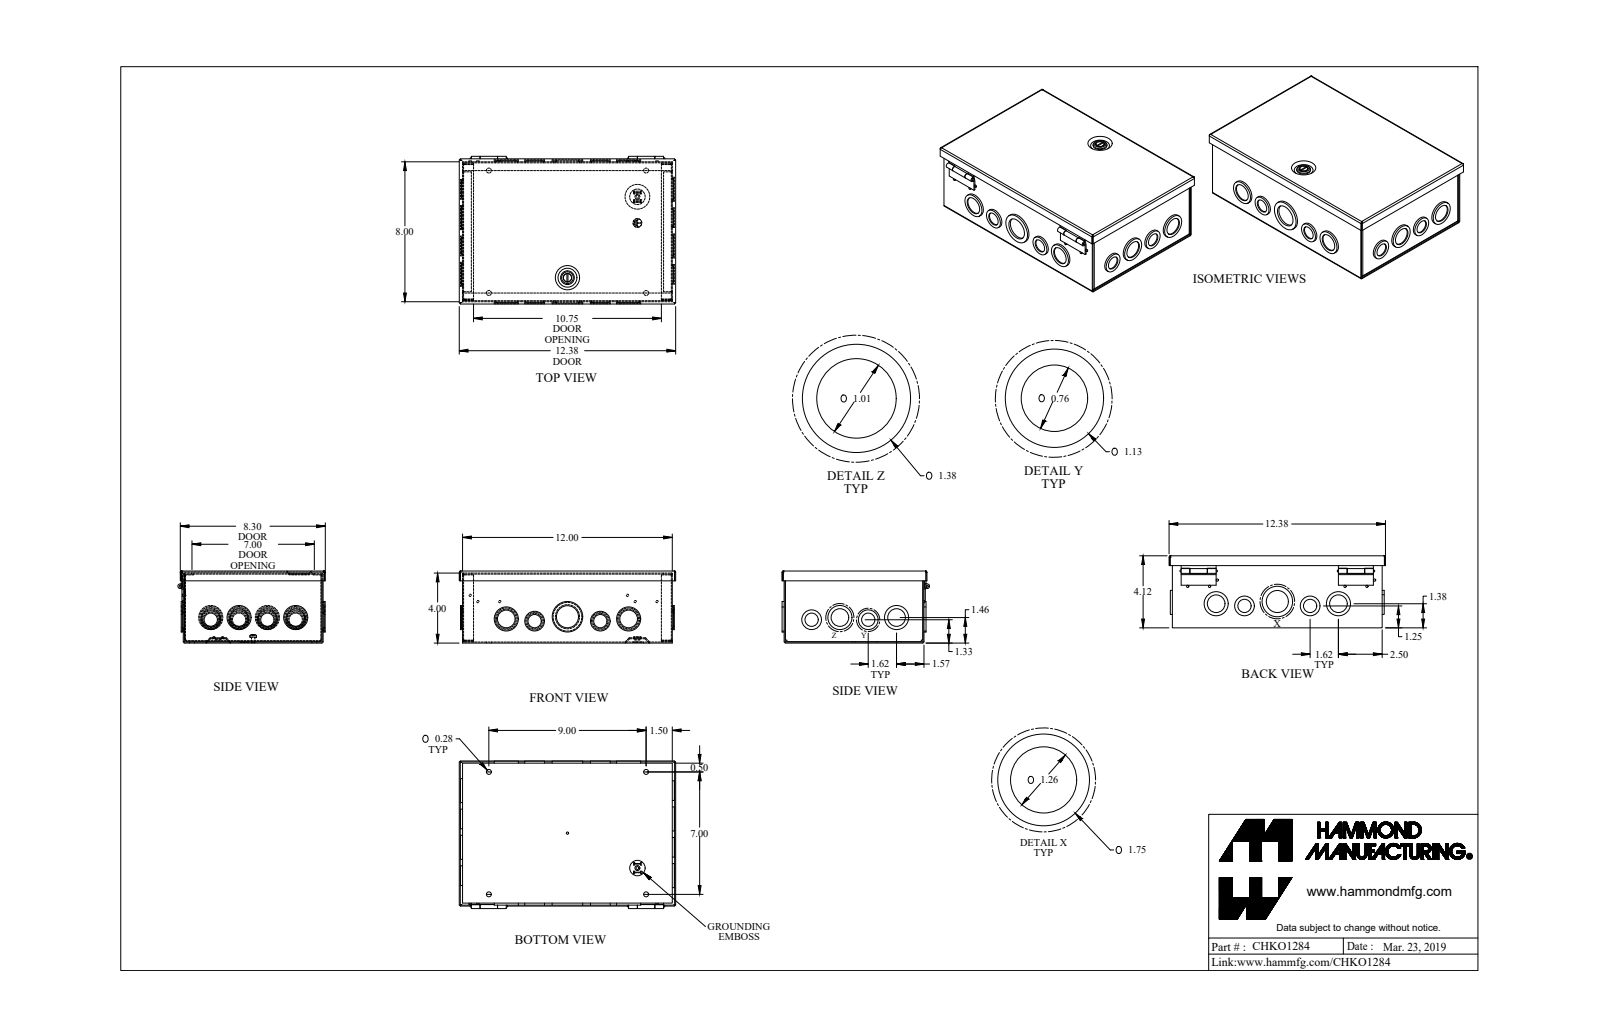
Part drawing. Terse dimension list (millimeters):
name: CHKO1284_Default
written by: SolidWorks 2019 (CONFIG_CONTROL_DESIGN)
unit: mm
bodies: 12 solids, 703 faces (344 planar, 316 cylindrical, 43 other)
size: 314.5 × 214.5 × 104.6
volume: 406 700 mm³; area: 563 800 mm²
holes: 12× ⌀25.7, 7× ⌀32, 6× ⌀19.3, 4× ⌀7.1, 1× ⌀3.2, 1× ⌀4.3, 1× ⌀8.1, 1× ⌀12.1, 1× ⌀12.7, 1× ⌀41.6
bosses: 8× ⌀28.6, 8× ⌀3.3, 7× ⌀34.9, 6× ⌀22.2, 4× ⌀28.6, 2× ⌀22.2, 1× ⌀44.5, 1× ⌀20
rounds: 16× R0.7, 16× R2.2, 8× R1.4, 4× R0.3, 4× R2.5, 2× R0.9, 2× R2, 2× R6.4
face distances: 1.4, 103.1, 104.6, 101.7, 201.8, 303.4, 203.2, 200.3, 304.8, 100.2
hole spacings: 41.3, 3.2, 41.1, 82.3, 82.3, 177.8, 41.1, 41.2
